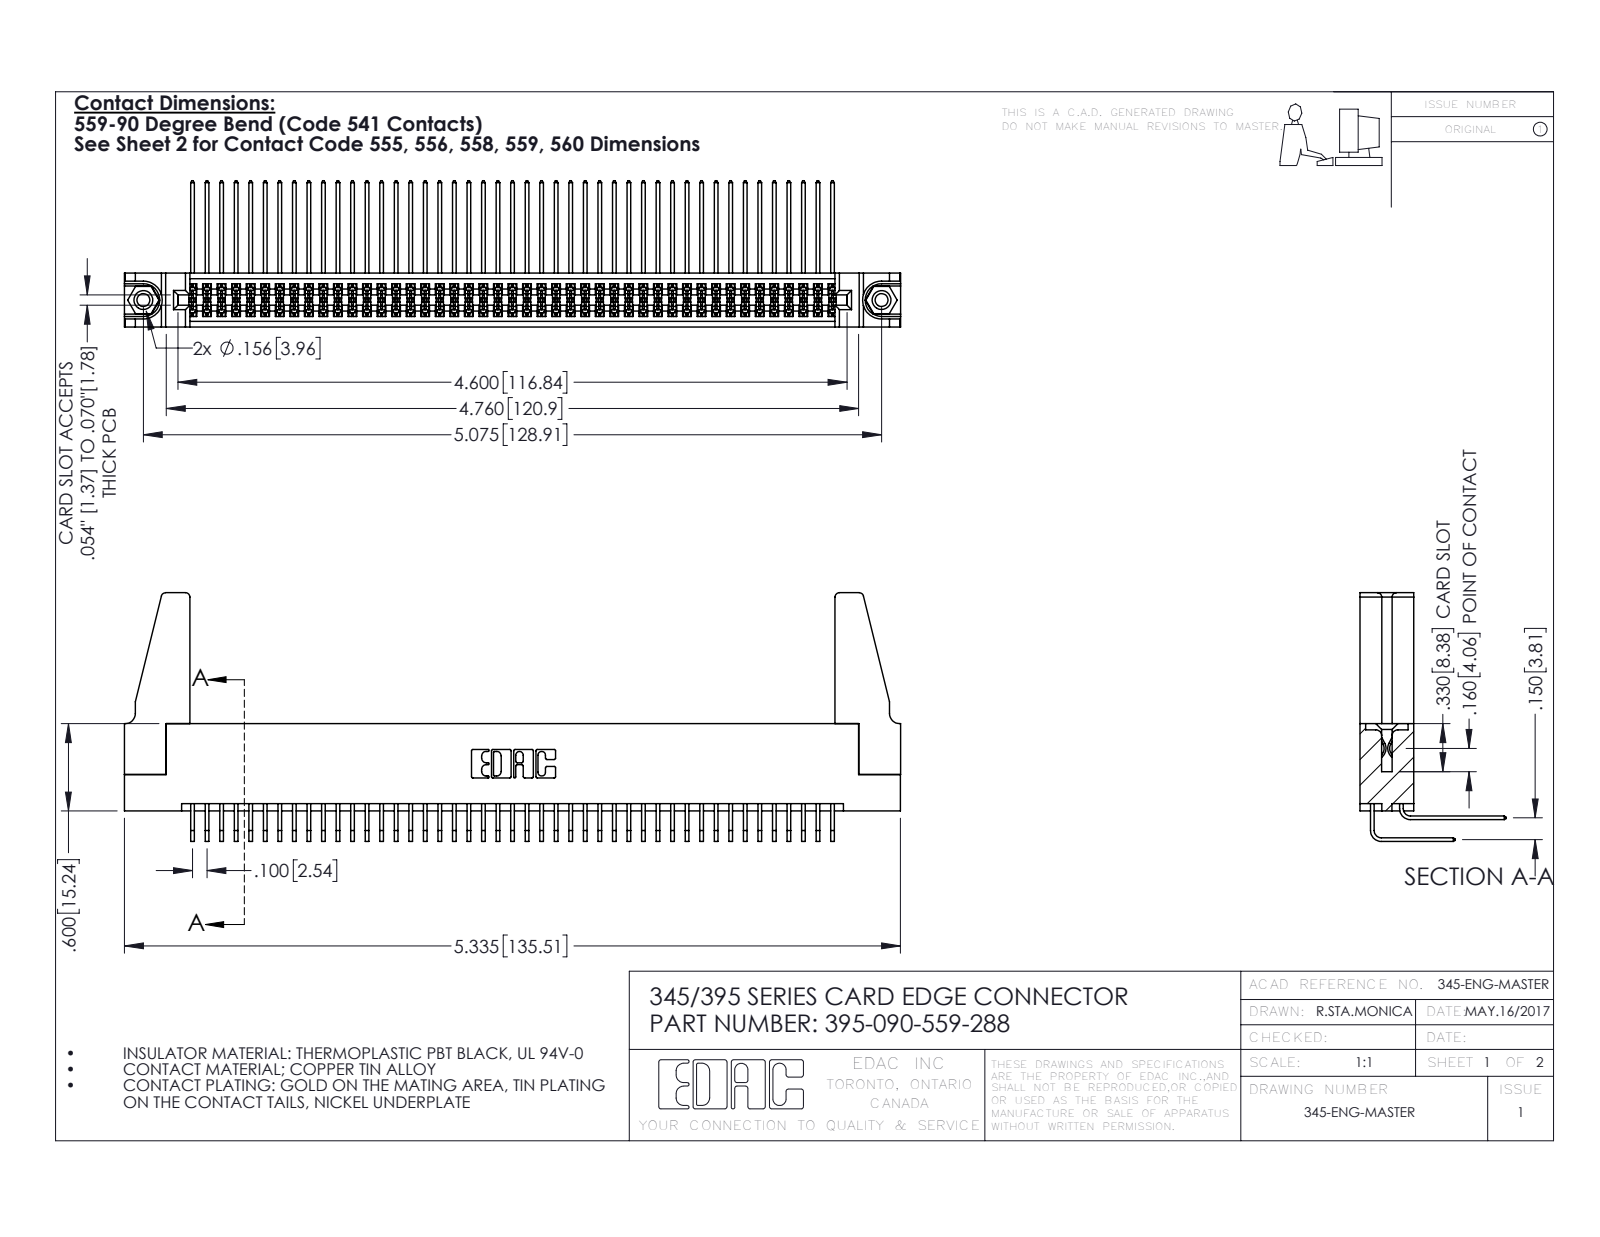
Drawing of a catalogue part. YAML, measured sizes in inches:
part_name: "345-250-001_345-250-001-102; 345 Part_Flush Mounting Lugs - 0.156 Dia-TH; 345-292-001_559 Tail - 2; 345-220-078_345-220-088 (+2 more)"
step_written_by: "SolidWorks 2016 (CONFIG_CONTROL_DESIGN)"
units: inches
bodies: {solids: 95, faces: 4930, planar: 3302, cylindrical: 1612, other: 16}
overall_size: [5.336, 1.709, 1.005]
volume: 1.035
surface_area: 40.13
round_holes:
  - {diameter: 0.089, count: 2}
  - {diameter: 0.125, count: 2}
  - {diameter: 0.156, count: 2}
  - {diameter: 0.064, count: 1}
round_bosses_or_shafts:
  - {diameter: 0.155, count: 2}
partial_cylinders:
  - {radius: 0.006, count: 136}
  - {radius: 0.01, count: 22}
  - {radius: 0.03, count: 8}
  - {radius: 0.007, count: 6}
  - {radius: 0.031, count: 6}
  - {radius: 0.026, count: 3}
  - {radius: 0.014, count: 2}
  - {radius: 0.019, count: 2}
face_to_face_distances: [0.072, 0.298, 0.37, 0.2, 0.098, 0.272, 0.025, 0.225, 0.175, 0.15]
hole_center_spacings: [0.27, 4.839, 5.075]
